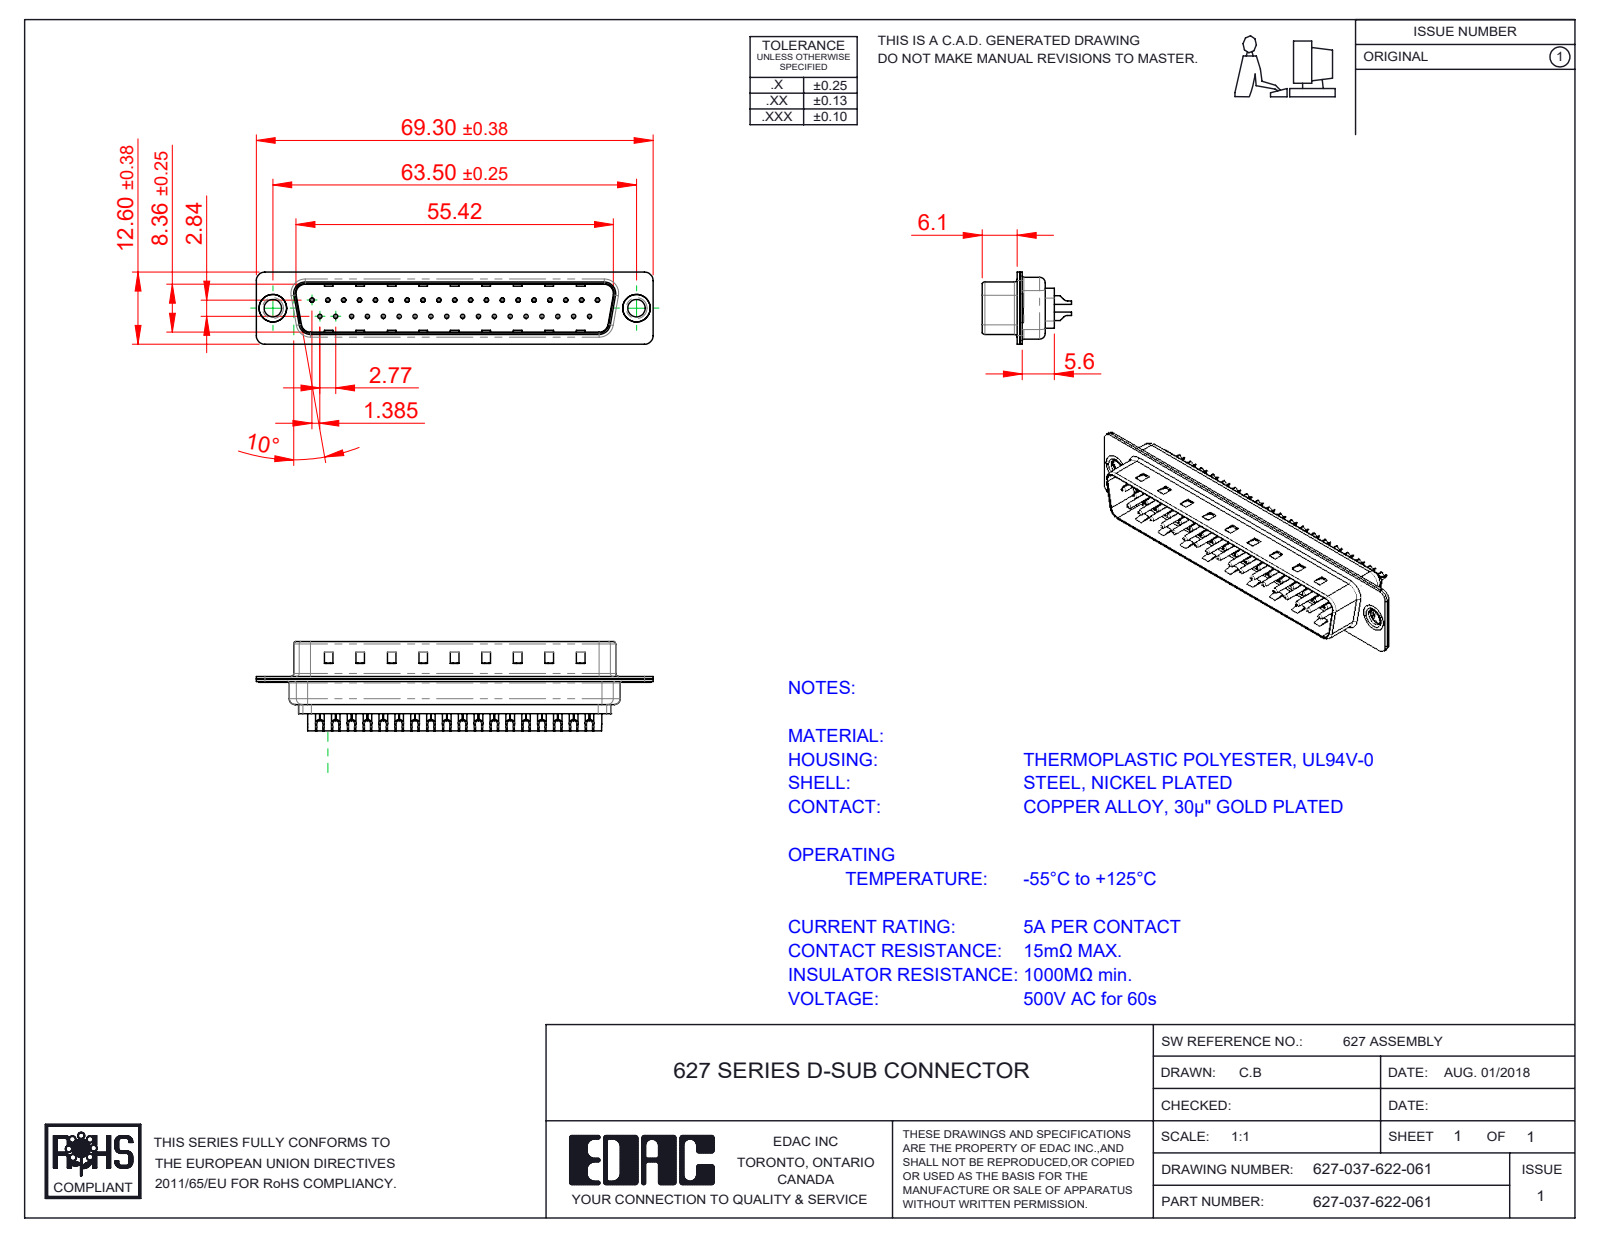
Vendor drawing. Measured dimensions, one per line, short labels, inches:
name: 627 Shell Front_37 Contacts; 627-037-622-061; 627 Thru Hole Rivet; 627 Shell Rear_37 Contacts (+3 more)
written by: SolidWorks 2020 (CONFIG_CONTROL_DESIGN)
unit: in
bodies: 42 solids, 2754 faces (721 planar, 1198 cylindrical, 835 other)
size: 2.728 × 0.604 × 0.496
volume: 0.222 in³; area: 16.45 in²
holes: 37× ⌀0.014, 37× ⌀0.043, 37× ⌀0.063, 2× ⌀0.12, 2× ⌀0.157, 2× ⌀0.189
bosses: 37× ⌀0.079, 37× ⌀0.059, 37× ⌀0.03, 2× ⌀0.197, 2× ⌀0.193, 2× ⌀0.14
rounds: 16× R0.059, 12× R0.079, 8× R0.02, 8× R0.063, 6× R0.039, 4× R0.01, 4× R0.024, 4× R0.026
face distances: 0.016, 0.032, 0.377, 0.018, 0.345, 0.035, 0.059, 0.055, 0.238, 0.02
hole spacings: 0.124, 0.109, 0.218, 0.327, 0.198, 0.398, 0.436, 0.503
